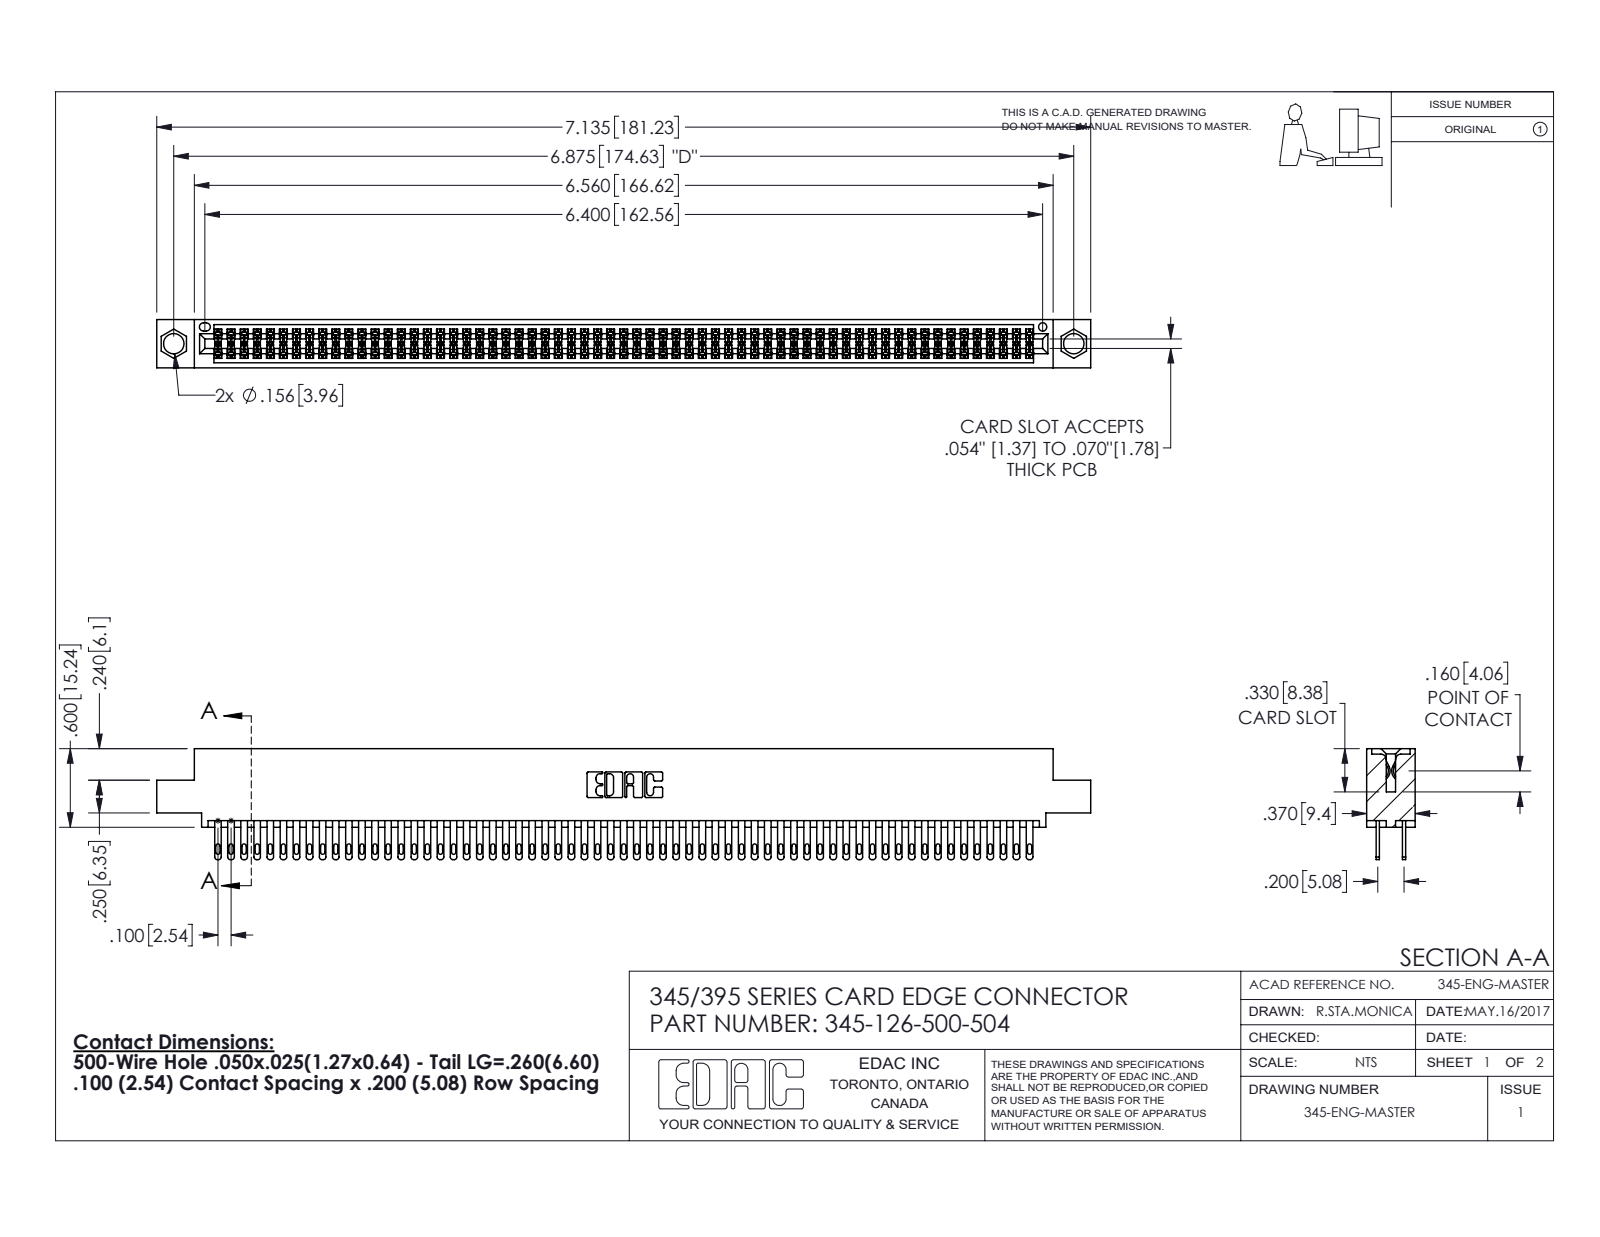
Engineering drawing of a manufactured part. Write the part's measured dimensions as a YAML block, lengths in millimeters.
part_name: "345-292-001_345-293-100; 345 Part_0.110 Offset - 0.156 Dia-TI; 345-126-500-504"
step_written_by: "SolidWorks 2020 (CONFIG_CONTROL_DESIGN)"
units: millimeters
bodies: {solids: 127, faces: 5940, planar: 3500, cylindrical: 2440, other: 0}
overall_size: [181.2, 21.5, 9.4]
volume: 18010
surface_area: 28250
round_holes:
  - {diameter: 4, count: 2}
  - {diameter: 1.6, count: 1}
partial_cylinders:
  - {radius: 0.2, count: 189}
  - {radius: 0.4, count: 126}
  - {radius: 0.5, count: 126}
  - {radius: 0.3, count: 22}
  - {radius: 0.2, count: 6}
  - {radius: 0.8, count: 6}
  - {radius: 0.7, count: 3}
  - {radius: 0.4, count: 2}
face_to_face_distances: [7.6, 1.8, 5.1, 2.5, 6.9, 0.6, 9.4, 5.7, 4.4, 3.8]
hole_center_spacings: [6.9, 168.6, 174.6]
